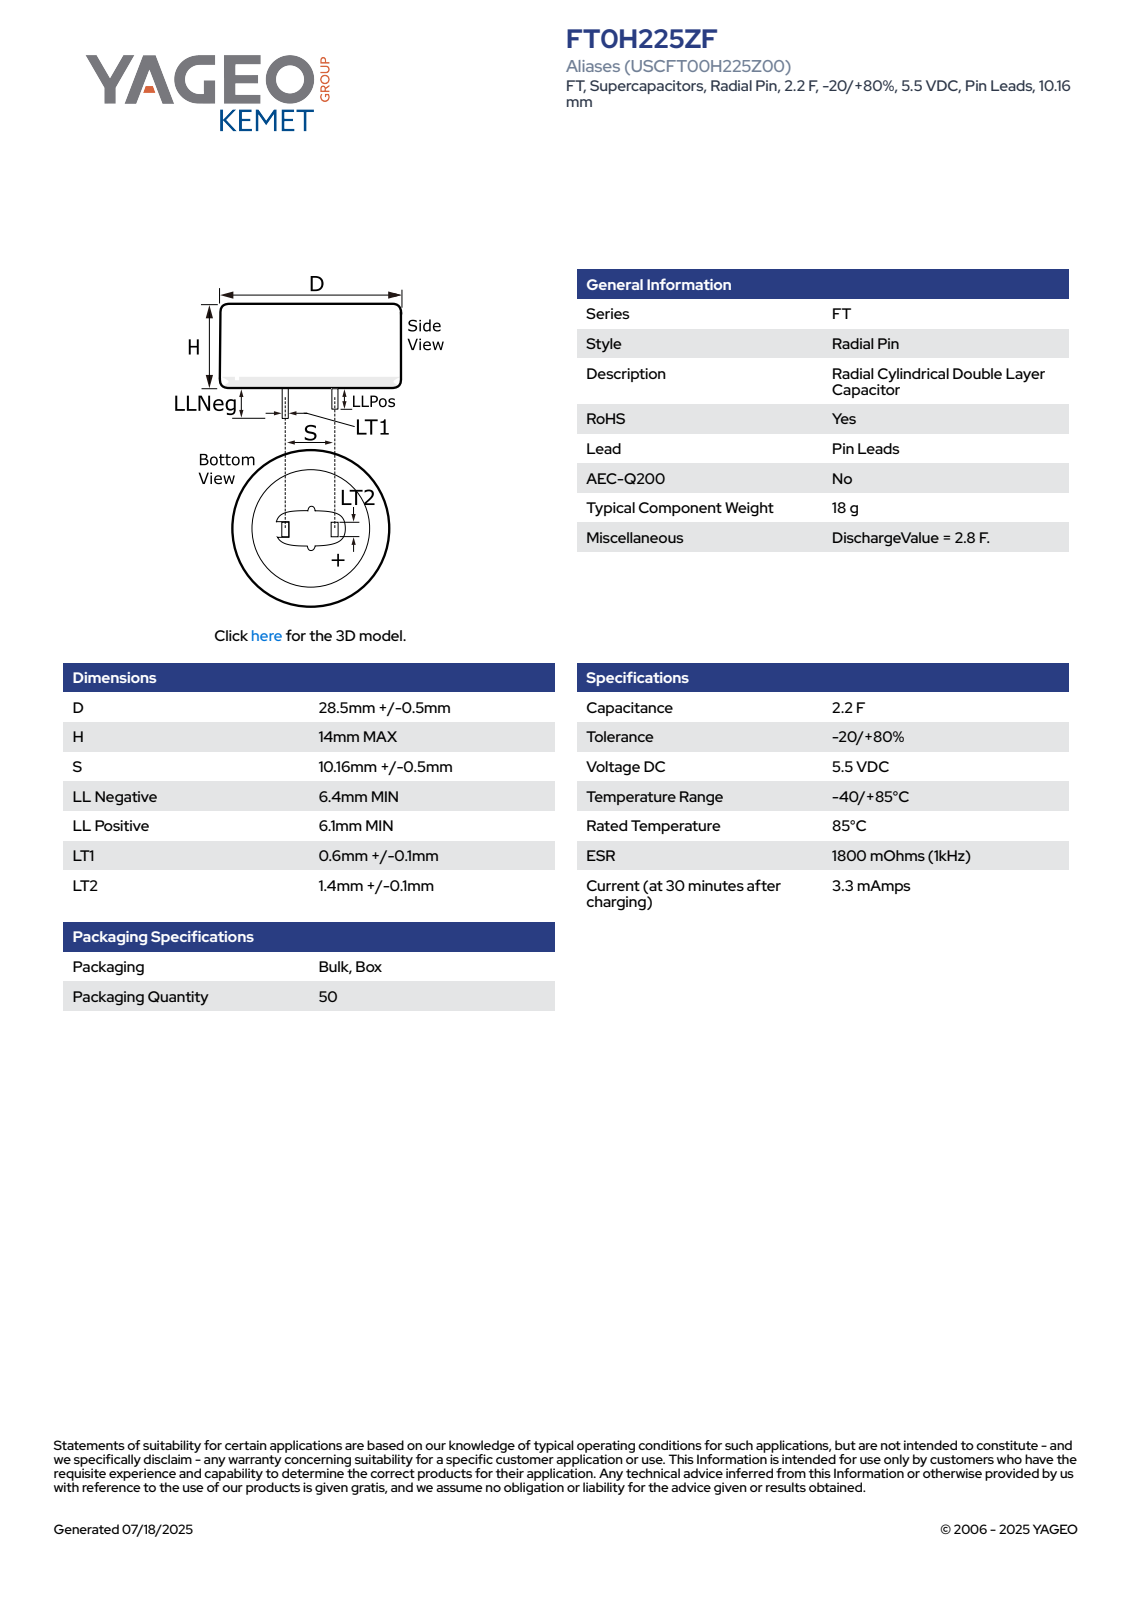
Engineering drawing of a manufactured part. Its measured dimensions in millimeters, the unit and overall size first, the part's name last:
Units: millimetres
Overall size (bounding box): 29 × 29 × 20.4
Round bosses / shafts (diameter × count): ⌀29 ×1
Partial cylindrical surfaces — rounded edges, fillets, slot ends (radius × count): R14.51 ×1
Main face-to-face distances: 14, 0.7, 10.16, 10.86, 9.46, 1.5, 6.4, 20.4, 6.1, 20.1
Volume: 9 229 mm³ · Surface area: 2 581 mm²
Bodies: 1 solid, 78 faces (70 planar, 4 cylindrical, 4 other)
Part name (STEP PRODUCT): CDR_LPLLN_D29L14S10.16LLNEG6.4LLPOS6.1LT10.7LT21.5
STEP written by: SolidWorks 2014 (AUTOMOTIVE_DESIGN)
